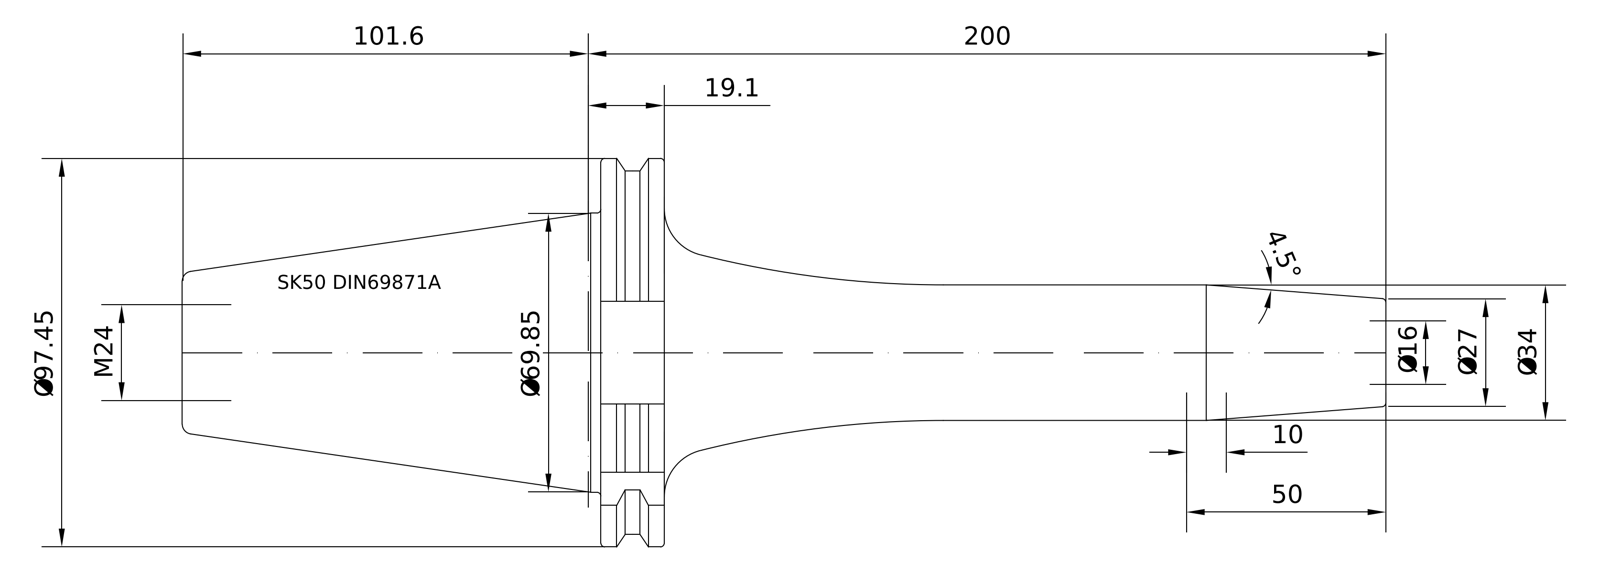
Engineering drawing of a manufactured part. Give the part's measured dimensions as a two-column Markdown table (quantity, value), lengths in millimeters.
| quantity | value |
| --- | --- |
| part name | 50-446-16 |
| STEP written by | PRO/ENGINEER BY PARAMETRIC TECHNOLOGY CORPORATION, 2010430 (CONFIG_CONTROL_DESIGN) |
| units | millimeters |
| bodies | 1 solid, 95 faces (21 planar, 24 cylindrical, 50 other) |
| overall size | 301.6 × 97.47 × 94 |
| volume | 517 802 mm³ |
| surface area | 63 438 mm² |
| round holes (diameter × count) | 16 × 1, 20.75 × 1, 25.01 × 1, 25.7 × 1 |
| round bosses / shafts (diameter × count) | 91 × 1, 69.15 × 1, 34 × 1, 24.01 × 1 |
| partial cylindrical surfaces (radius × count) | 1.75 × 1, 48.74 × 1 |
| main face-to-face distances | 15.85, 72.8, 104.8, 120.65, 25.8, 301.6, 196.8, 180.95, 251.6, 146.8 |
